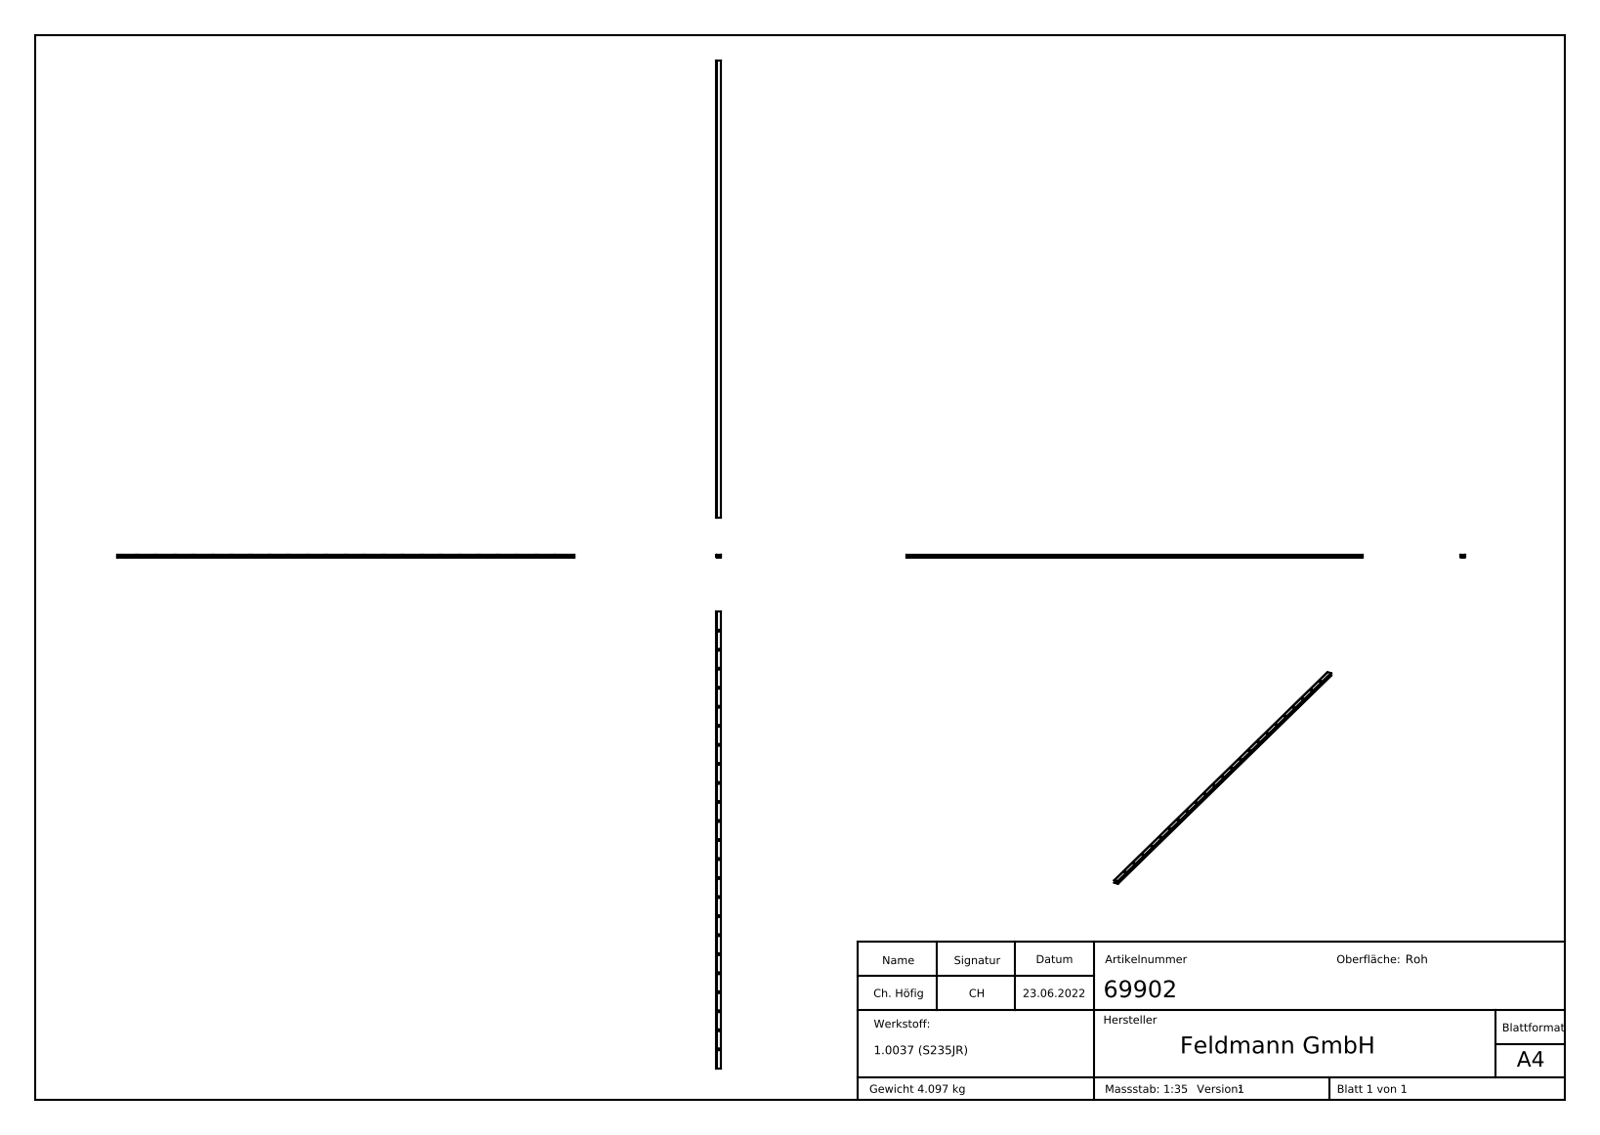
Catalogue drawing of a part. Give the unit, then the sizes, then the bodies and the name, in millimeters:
Units: millimetres
Overall size (bounding box): 3000 × 30 × 20
Round holes (diameter × count): ⌀13 ×23
Partial cylindrical surfaces — rounded edges, fillets, slot ends (radius × count): R1 ×4, R3 ×4
Main face-to-face distances: 2, 18, 28, 16, 20, 30, 26, 3000, 1.9, 26.1
Hole centre spacings: 125, 250, 375, 500, 625, 750, 875, 1000
Volume: 525 292 mm³ · Surface area: 527 536 mm²
Bodies: 1 solid, 263 faces (122 planar, 31 cylindrical, 110 other)
Part name (STEP PRODUCT): 69902
STEP written by: SolidWorks 2018 (CONFIG_CONTROL_DESIGN)
